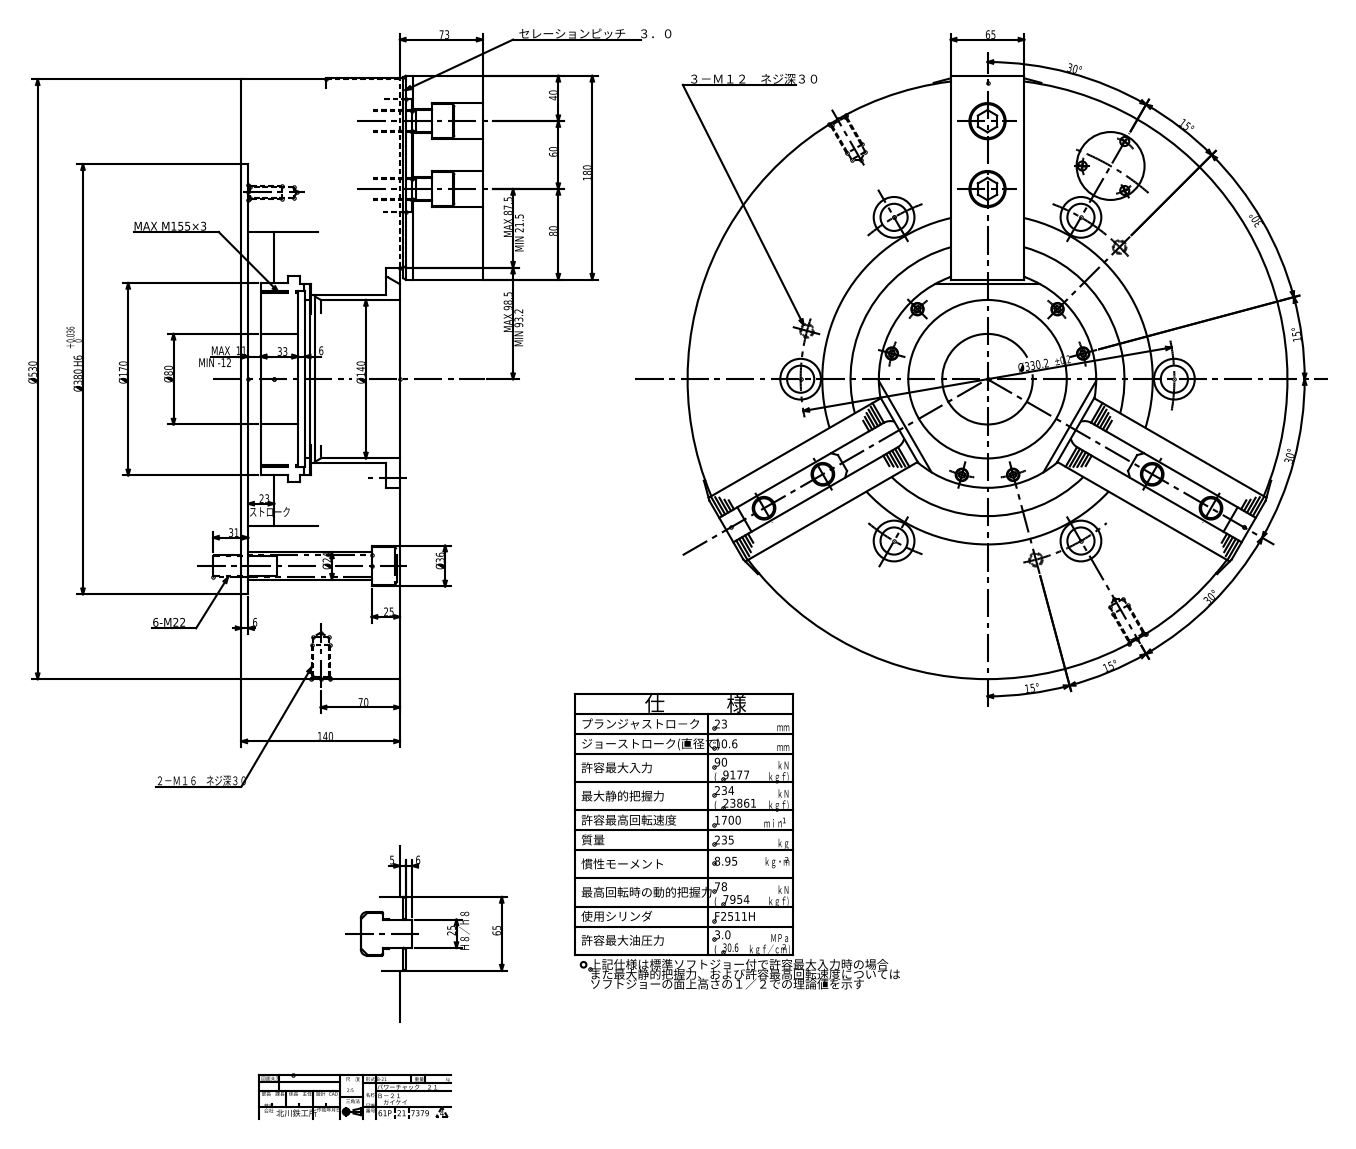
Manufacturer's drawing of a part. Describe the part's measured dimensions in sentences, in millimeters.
Its 3-D file was written by "Unknown (AUTOMOTIVE_DESIGN)". It is 1 solid with 4388 faces: 3616 planar, 392 cylindrical and 380 other. Overall it measures 551 by 530 by 238 millimeters. Its volume is 29 140 000 cubic millimeters and its surface area 1 568 000 square millimeters. Round holes: 9 of diameter 5.19, 9 of diameter 10.11, 6 of diameter 3.8, 6 of diameter 5, 6 of diameter 6.6, 6 of diameter 11, 6 of diameter 13.5, 6 of diameter 20, 6 of diameter 21, 6 of diameter 24, 6 of diameter 32, 6 of diameter 36. Round bosses or shafts: 12 of diameter 20, 6 of diameter 33, 6 of diameter 30, 6 of diameter 18, 6 of diameter 12, 6 of diameter 10, 6 of diameter 6, 3 of diameter 8. Partial cylindrical surfaces (rounded edges, fillets, slot ends): 18 of radius 1, 12 of radius 0.45, 12 of radius 0.6, 12 of radius 0.8, 6 of radius 0.5, 6 of radius 1.8, 6 of radius 2, 6 of radius 3.1. The main face-to-face distances are 140, 6, 134, 65, 12, 29, 99, 60, 20, 40. The hole center spacings are 40.03, 73.36, 87.5, 165.1, 186.91, 222.17, 229.22, 238.81.
